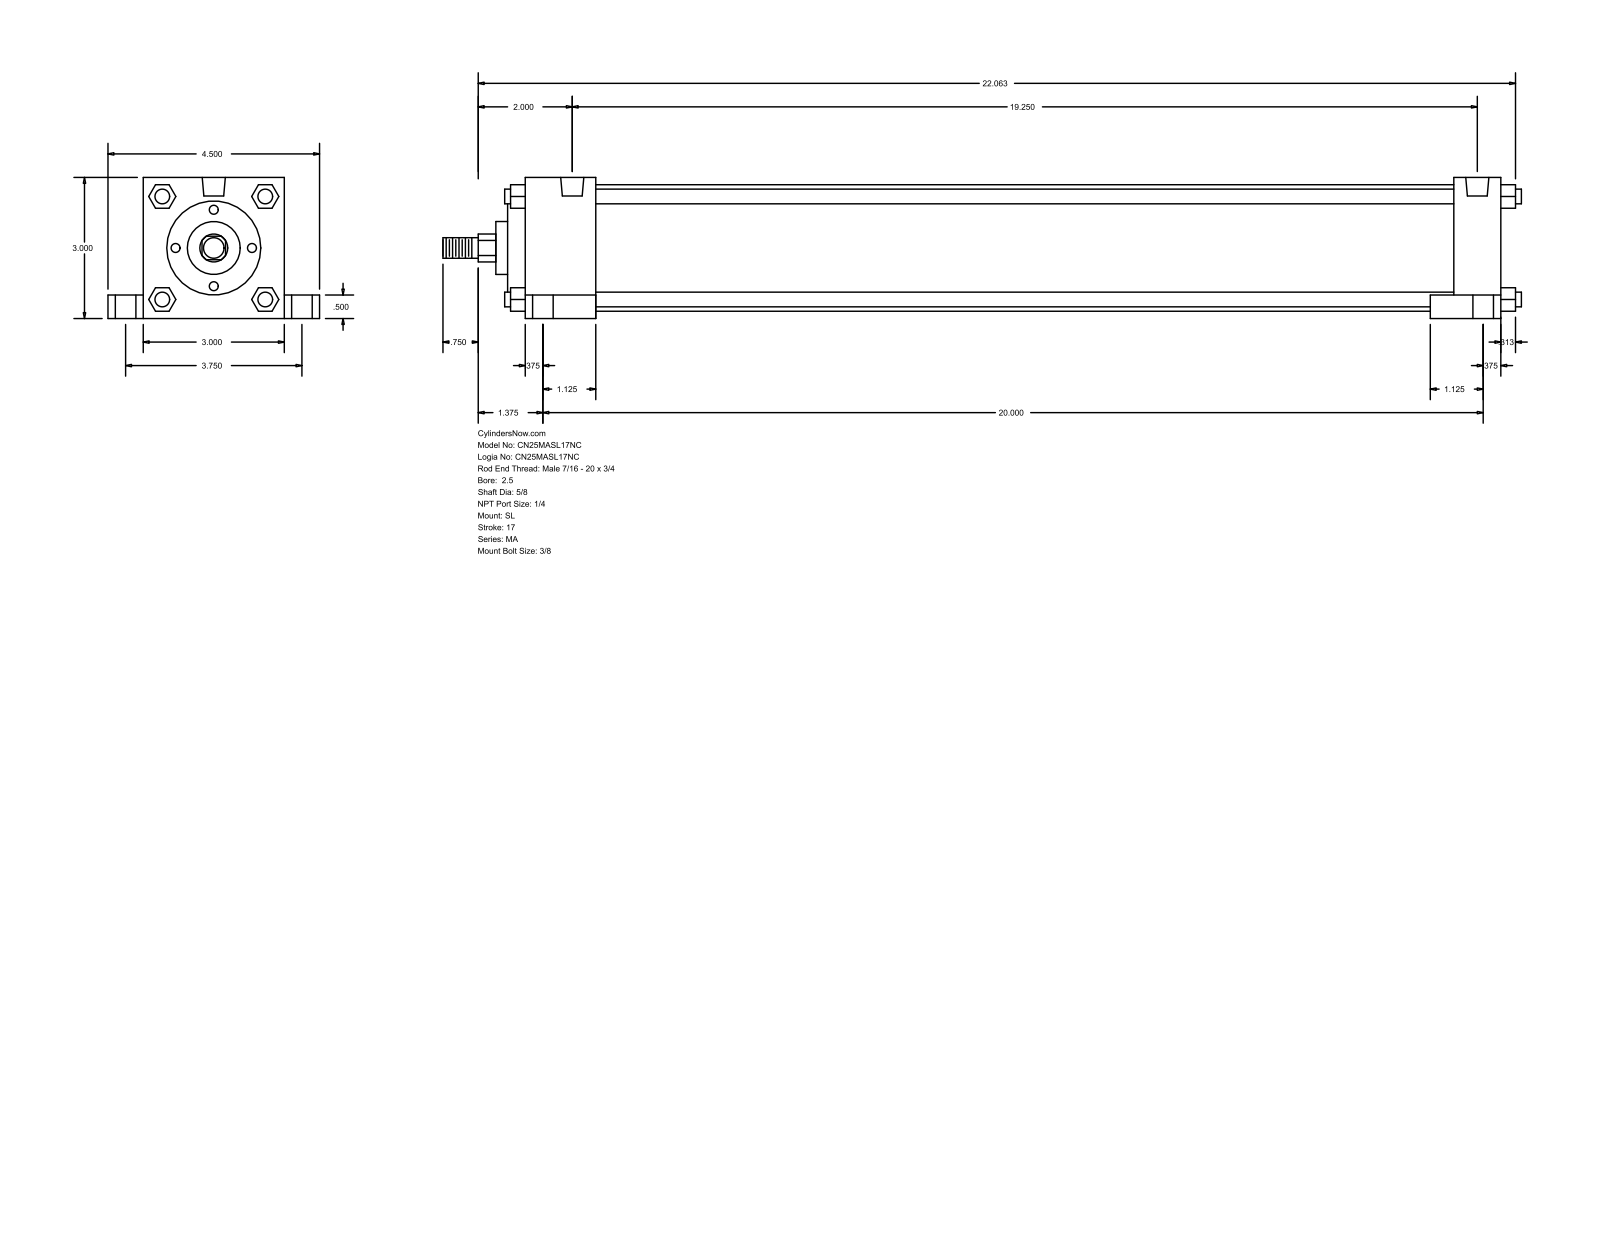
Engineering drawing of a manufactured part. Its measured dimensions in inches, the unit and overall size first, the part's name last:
Units: inches
Overall size (bounding box): 22.937 × 4.5 × 3
Round holes (diameter × count): ⌀0.313 ×4, ⌀0.437 ×4, ⌀0.687 ×4, ⌀0.492 ×2
Round bosses / shafts (diameter × count): ⌀0.313 ×4, ⌀2.69 ×1, ⌀2 ×1, ⌀1.125 ×1, ⌀0.625 ×1, ⌀0.437 ×1
Partial cylindrical surfaces — rounded edges, fillets, slot ends (radius × count): R0.297 ×1
Main face-to-face distances: 3, 20.75, 0.5, 18.25, 1, 1.5, 19.25, 19.75, 0.75, 2.5
Hole centre spacings: 1.879, 1.976, 3.75, 19.25, 19.465, 19.963, 20, 20.348
Bodies: 0 solids, 150 faces (113 planar, 37 cylindrical, 0 other)
Part name (STEP PRODUCT): MA_SL__0250_0.625
STEP written by: GSSL Pune (CONFIG_CONTROL_DESIGN)
